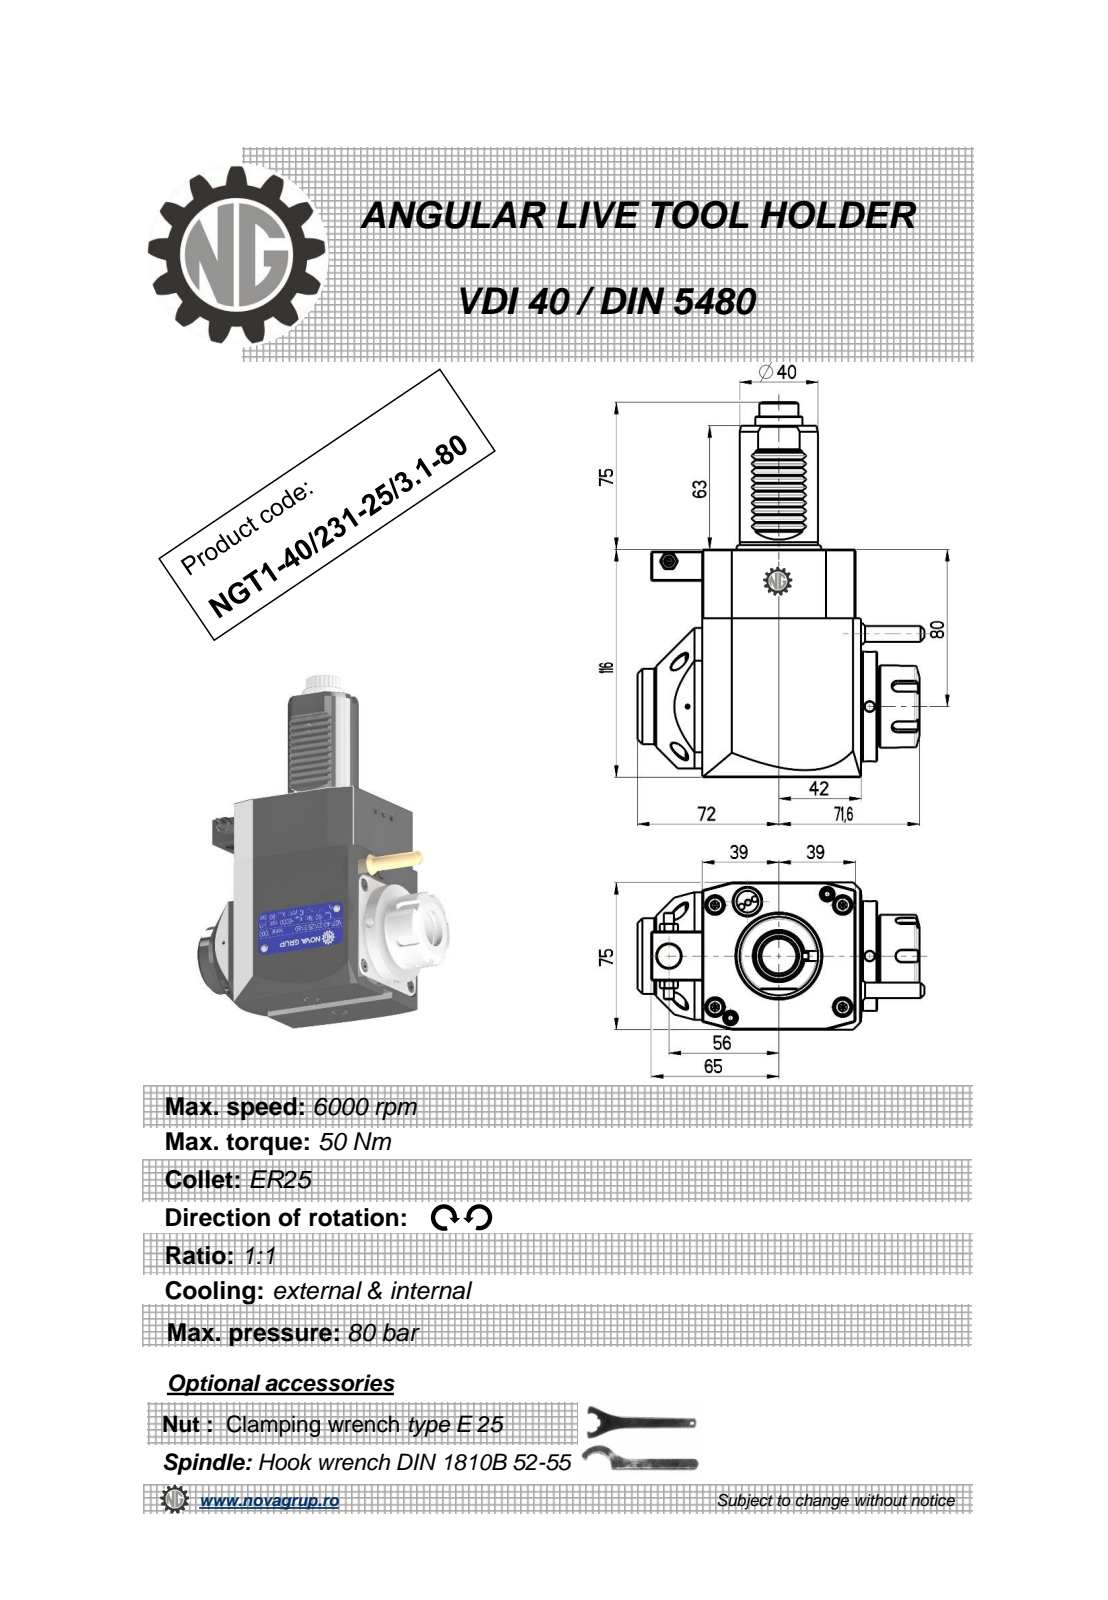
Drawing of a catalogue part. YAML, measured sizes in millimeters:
part_name: "NGT1_40_231_25_3_1_80"
step_written_by: "PRO/ENGINEER BY PARAMETRIC TECHNOLOGY CORPORATION, 2010280 (CONFIG_CONTROL_DESIGN)"
units: millimeters
bodies: {solids: 1, faces: 549, planar: 193, cylindrical: 183, other: 173}
overall_size: [191, 146.14, 75]
volume: 897258
surface_area: 72176
round_holes:
  - {diameter: 5, count: 3}
  - {diameter: 3, count: 1}
  - {diameter: 4.2, count: 1}
  - {diameter: 9.5, count: 1}
  - {diameter: 12, count: 1}
  - {diameter: 20.3, count: 1}
round_bosses_or_shafts:
  - {diameter: 56, count: 1}
  - {diameter: 43, count: 1}
  - {diameter: 42, count: 1}
  - {diameter: 40, count: 1}
  - {diameter: 38.5, count: 1}
  - {diameter: 33, count: 1}
  - {diameter: 24, count: 1}
  - {diameter: 11.2, count: 1}
partial_cylinders:
  - {radius: 2.08, count: 48}
  - {radius: 0.26, count: 12}
  - {radius: 0.3, count: 10}
  - {radius: 0.22, count: 6}
  - {radius: 3, count: 5}
  - {radius: 9.08, count: 1}
  - {radius: 9.92, count: 1}
  - {radius: 15, count: 1}
face_to_face_distances: [75, 116, 81, 78, 3, 11, 8, 7.5, 80.8, 2.8]
hole_center_spacings: [38.68, 40.93, 71.5, 102.25, 126.22]
